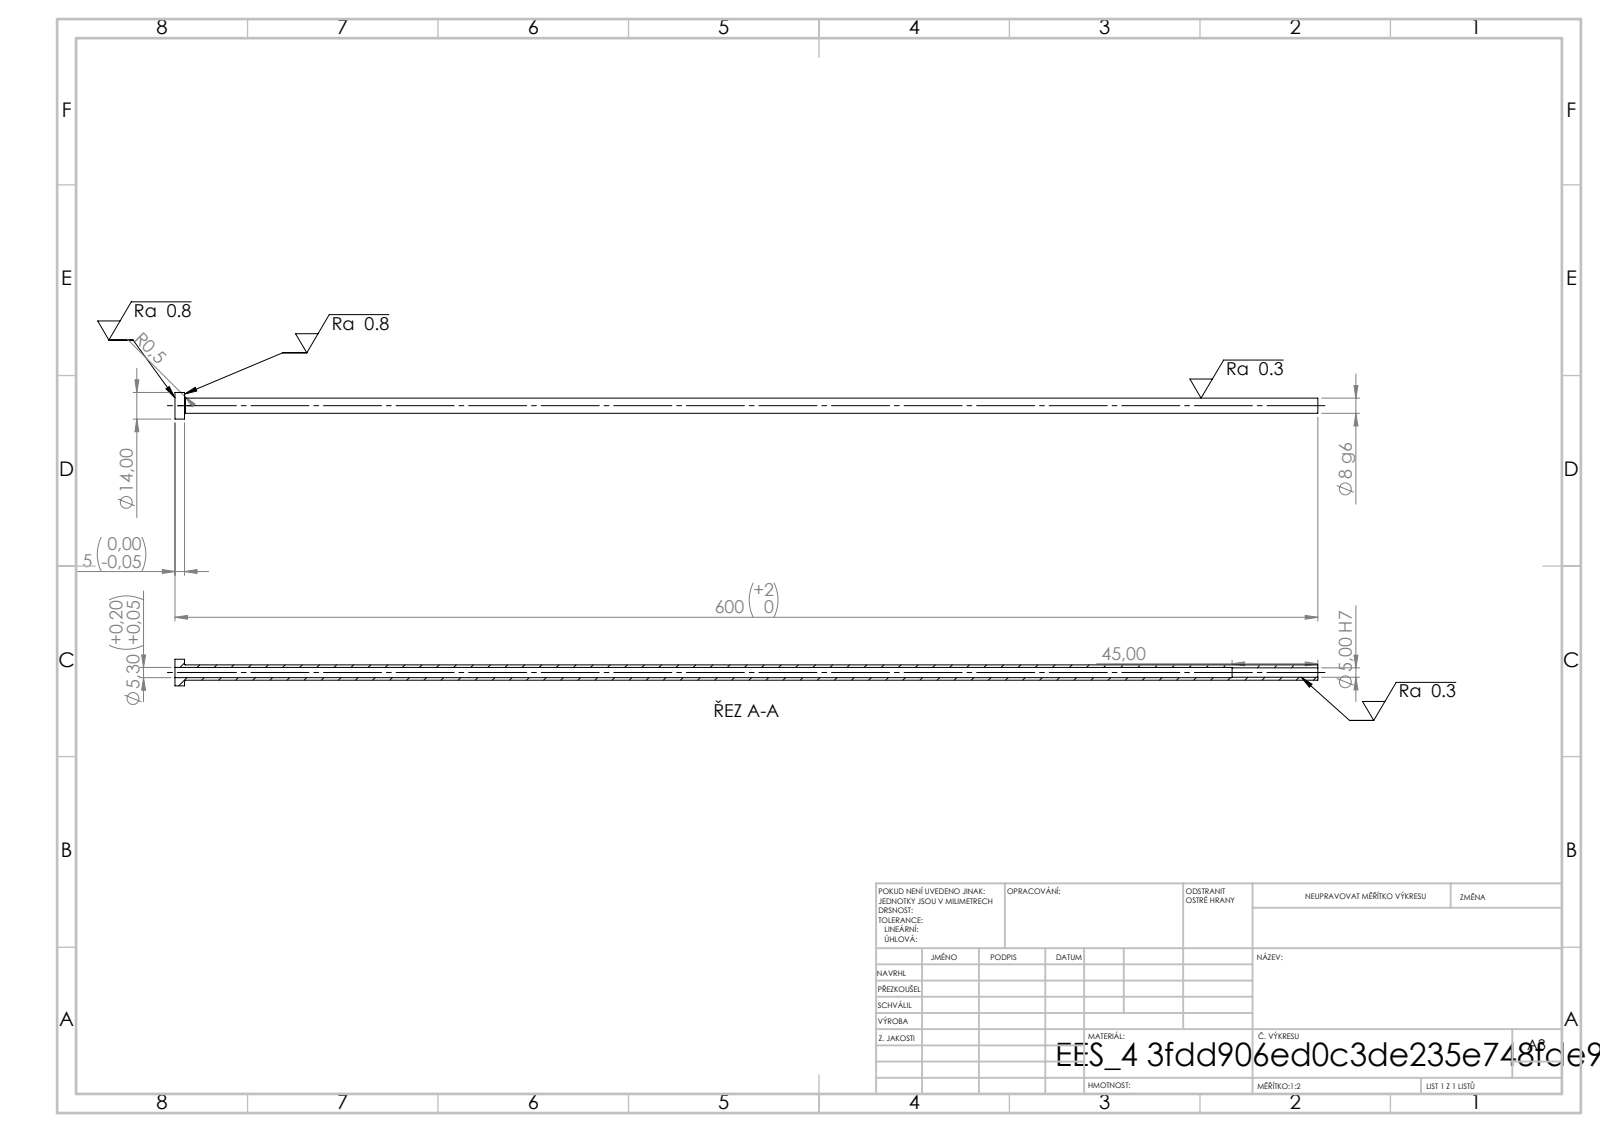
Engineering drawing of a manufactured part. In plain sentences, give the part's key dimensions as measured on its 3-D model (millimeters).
Its 3-D file was written by "SolidWorks 2019 (CONFIG_CONTROL_DESIGN)". It is 1 solid with 14 faces: 4 planar, 8 cylindrical and 2 other. Overall it measures 600 by 14 by 14 millimeters. Its volume is 17 551 cubic millimeters and its surface area 25 385 square millimeters. Round holes: 1 of diameter 5, 1 of diameter 5.3. Round bosses or shafts: 1 of diameter 14, 1 of diameter 8. The main face-to-face distances are 5, 600, 595, 555, 550, 45.
